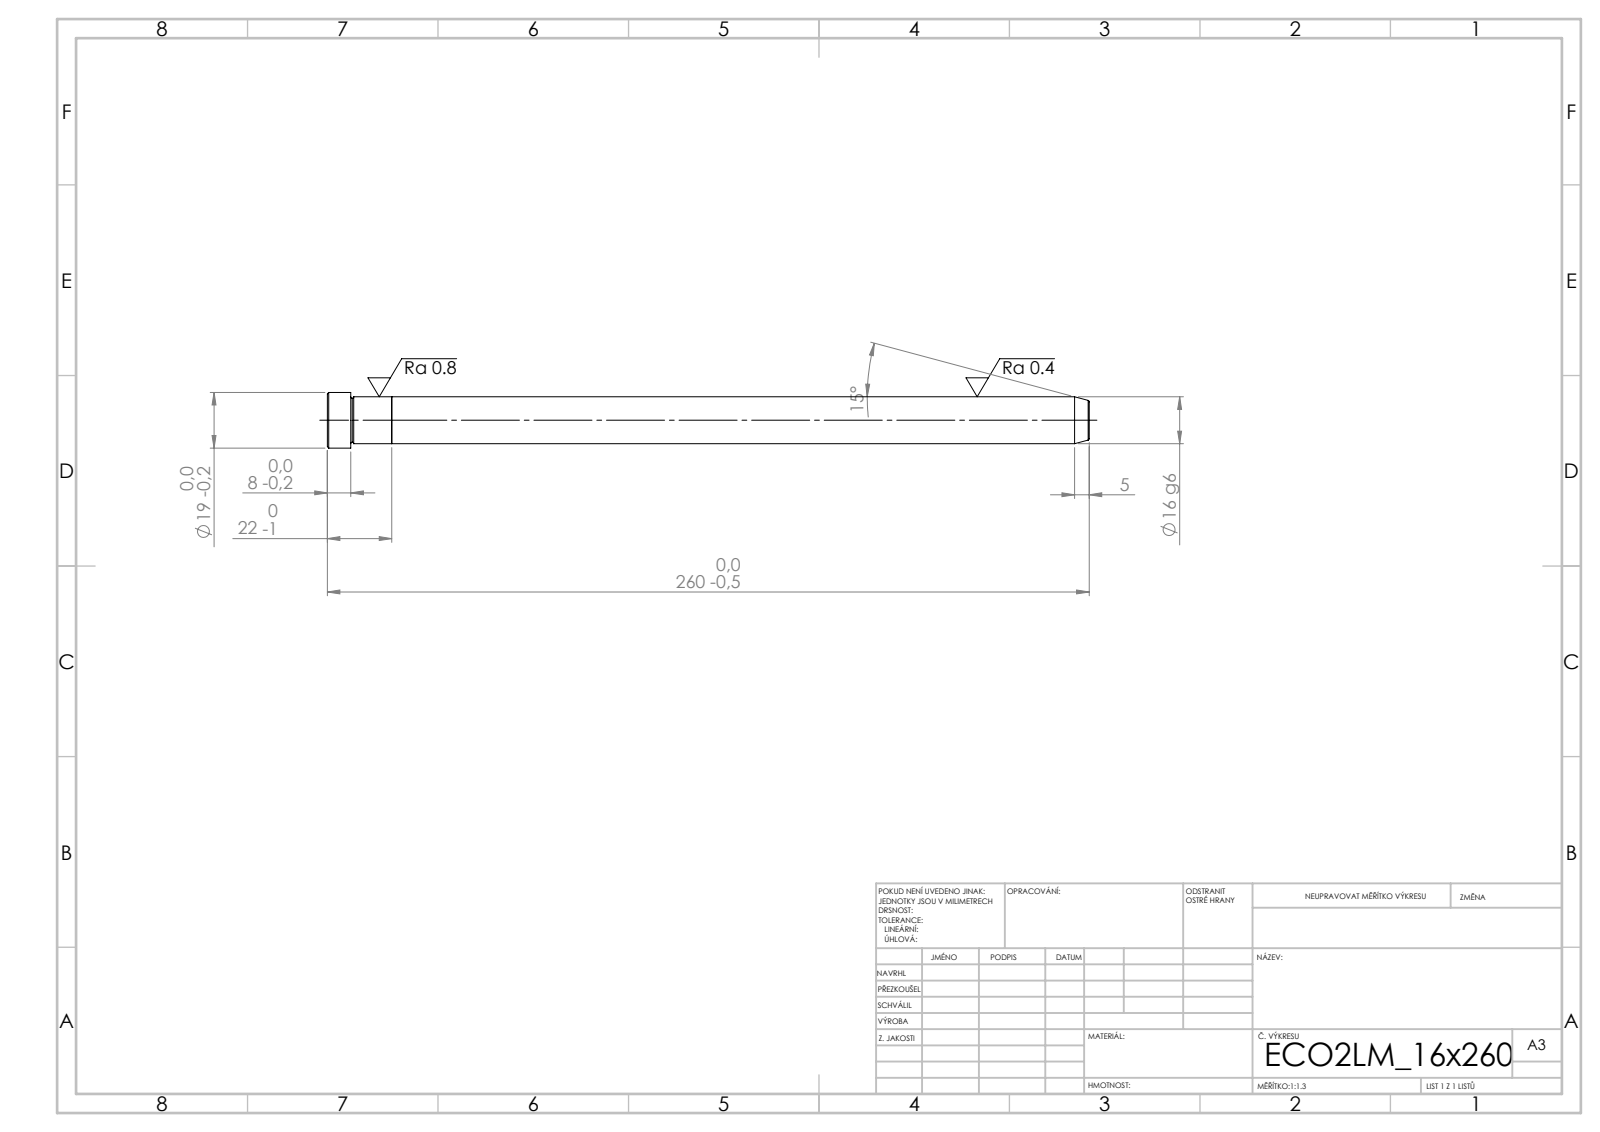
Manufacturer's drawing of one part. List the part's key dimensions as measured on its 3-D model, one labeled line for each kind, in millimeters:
STEP written by: SolidWorks 2019 (CONFIG_CONTROL_DESIGN)
Units: millimetres
Bodies: 2 solids, 21 faces (5 planar, 6 cylindrical, 10 other)
Overall size (bounding box): 260 × 19 × 19
Volume: 52 749 mm³ · Surface area: 14 042 mm²
Round bosses / shafts (diameter × count): ⌀19 ×1, ⌀16 ×1
Main face-to-face distances: 22, 238, 260, 252, 14, 8
